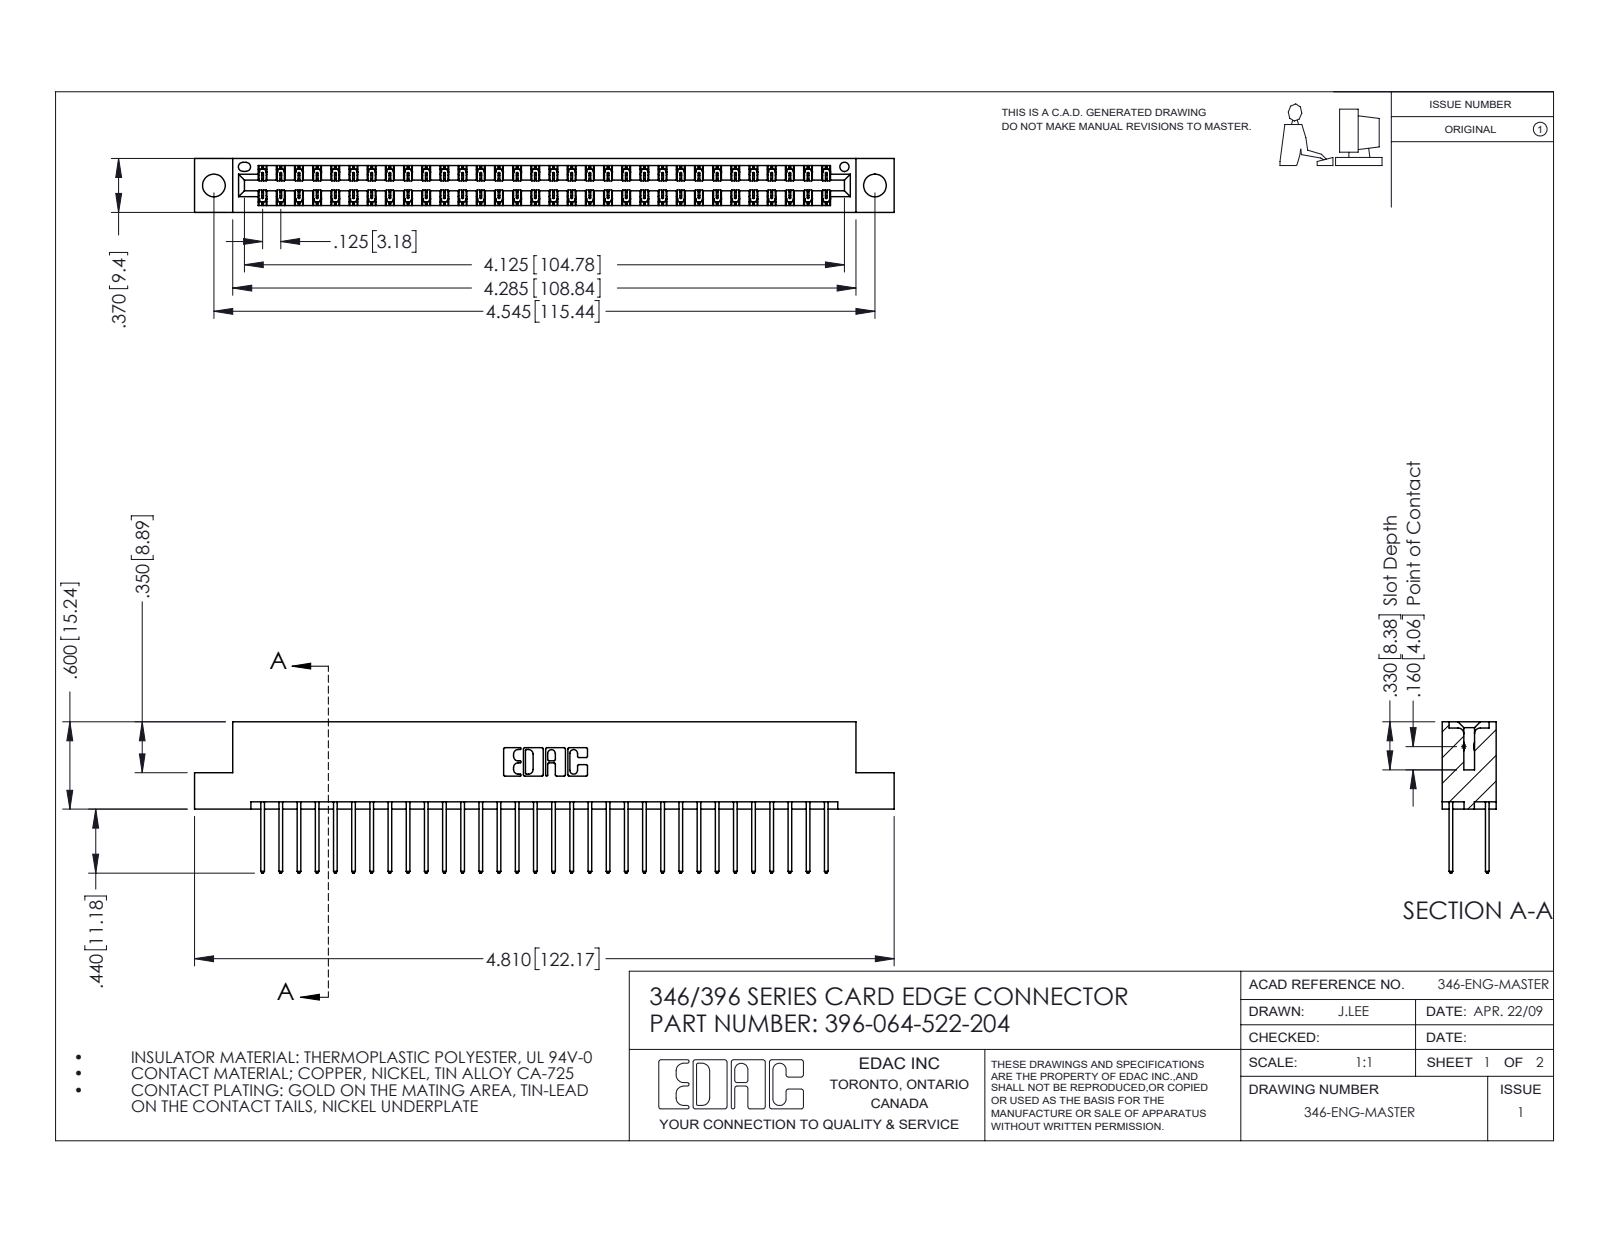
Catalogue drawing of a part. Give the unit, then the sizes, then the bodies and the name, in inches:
Units: inches
Overall size (bounding box): 4.81 × 1.04 × 0.37
Round holes (diameter × count): ⌀0.156 ×2, ⌀0.064 ×1
Partial cylindrical surfaces — rounded edges, fillets, slot ends (radius × count): R0.006 ×96, R0.01 ×64, R0.01 ×22, R0.007 ×6, R0.031 ×6, R0.026 ×3, R0.014 ×2, R0.022 ×2
Main face-to-face distances: 0.048, 0.322, 0.25, 0.37, 0.072, 0.298, 0.025, 0.275, 0.148, 0.222
Hole centre spacings: 0.246, 4.337, 4.545
Volume: 0.727 in³ · Surface area: 26.02 in²
Bodies: 65 solids, 3450 faces (2316 planar, 1134 cylindrical, 0 other)
Part name (STEP PRODUCT): 345-292-001_345-293-122; 396-064-522-204; 346 Part_Flush Mounting Lugs - 0.156 Dia-TH
STEP written by: SolidWorks 2016 (CONFIG_CONTROL_DESIGN)
